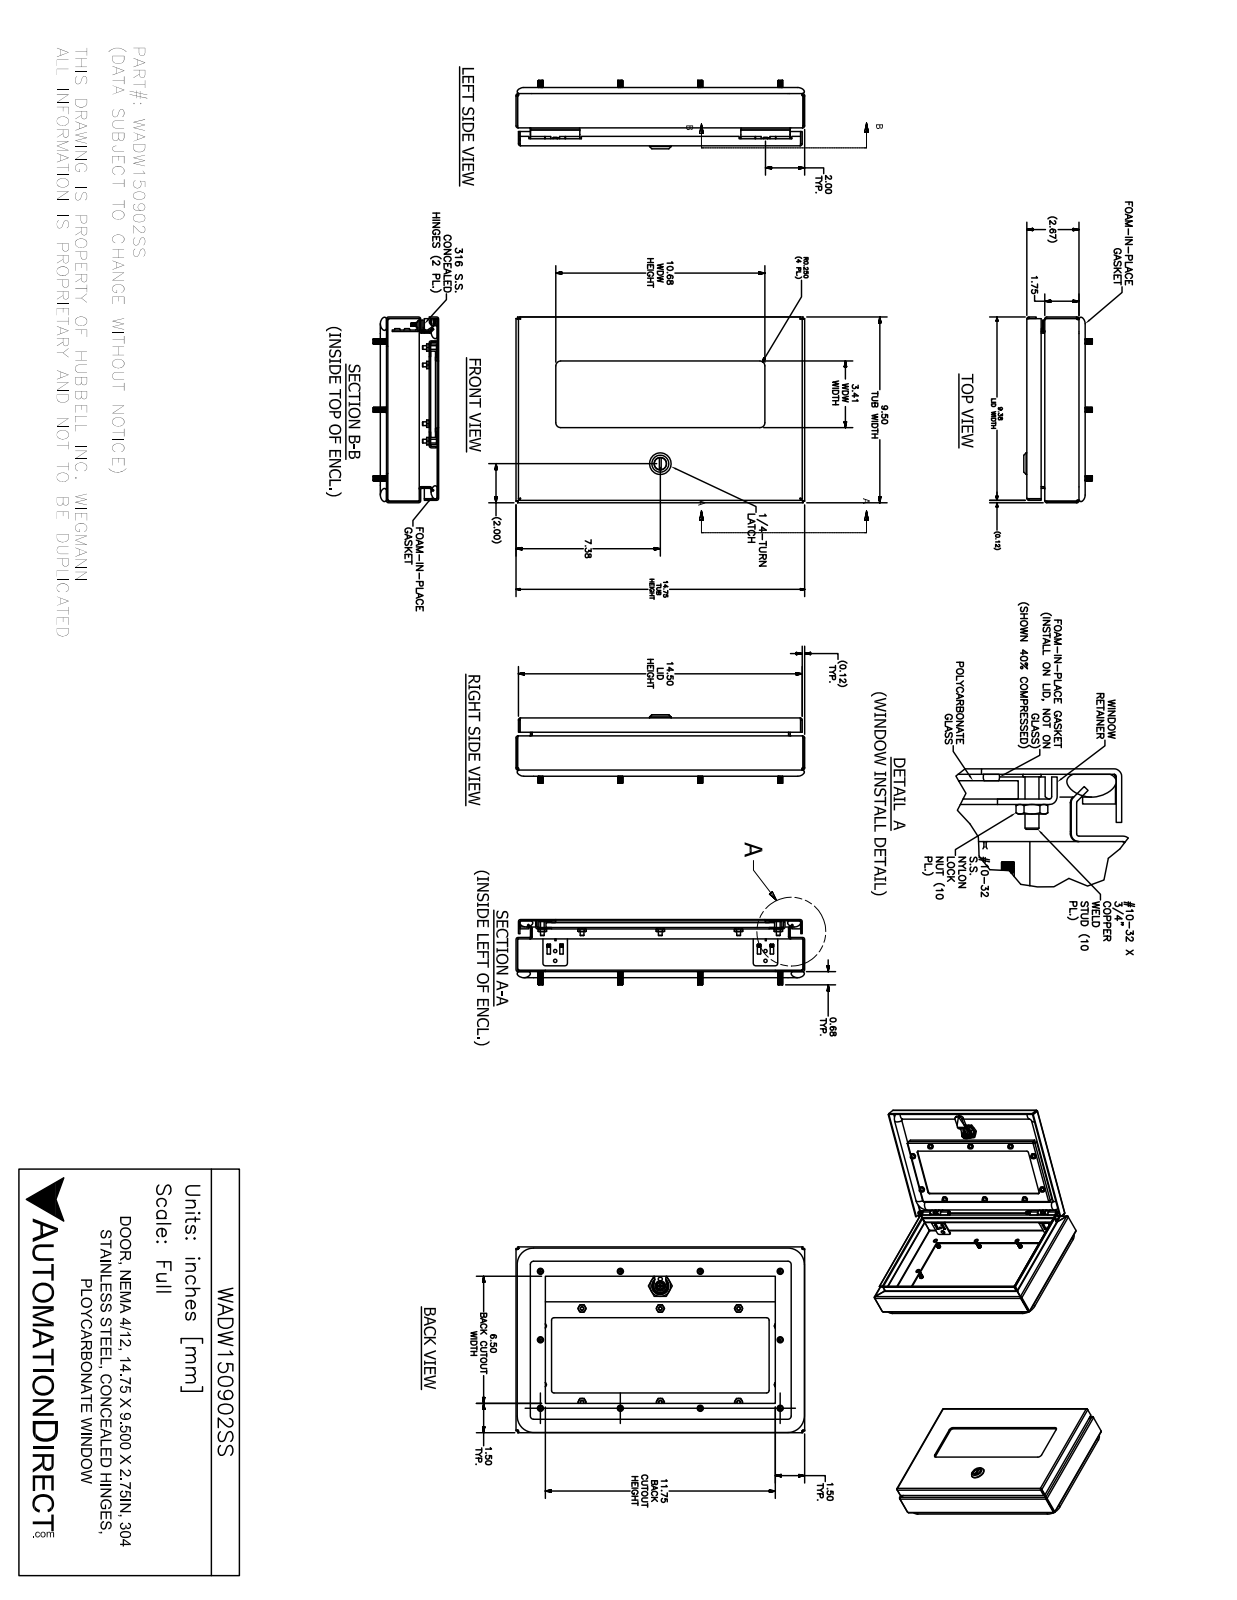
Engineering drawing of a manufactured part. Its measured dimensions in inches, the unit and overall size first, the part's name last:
Units: inches
Overall size (bounding box): 14.75 × 9.5 × 3.501
Round holes (diameter × count): ⌀0.156 ×12, ⌀0.249 ×10, ⌀0.281 ×10, ⌀0.093 ×4, ⌀0.152 ×4, ⌀0.167 ×4, ⌀0.172 ×4, ⌀0.188 ×4, ⌀0.187 ×1, ⌀0.197 ×1, ⌀0.315 ×1, ⌀0.394 ×1
Round bosses / shafts (diameter × count): ⌀0.25 ×28, ⌀0.32 ×10, ⌀0.313 ×10, ⌀0.19 ×10, ⌀0.188 ×10, ⌀0.36 ×4, ⌀0.32 ×4, ⌀0.256 ×4
Partial cylindrical surfaces — rounded edges, fillets, slot ends (radius × count): R0.031 ×34, R0.012 ×30, R0.05 ×26, R0.105 ×24, R0.125 ×20, R0.016 ×18, R0.02 ×13, R0.032 ×8
Main face-to-face distances: 0.074, 2.593, 0.411, 2.182, 2.667, 2.256, 0.337, 1.676, 2.519, 0.25
Hole centre spacings: 8.104, 10.746, 3.5, 4, 4.083, 5.378, 6.237, 7
Volume: 58.1 in³ · Surface area: 1 104 in²
Bodies: 63 solids, 2144 faces (739 planar, 778 cylindrical, 627 other)
Part name (STEP PRODUCT): WADW150902SS
STEP written by: SolidWorks 2017 (AUTOMOTIVE_DESIGN)
